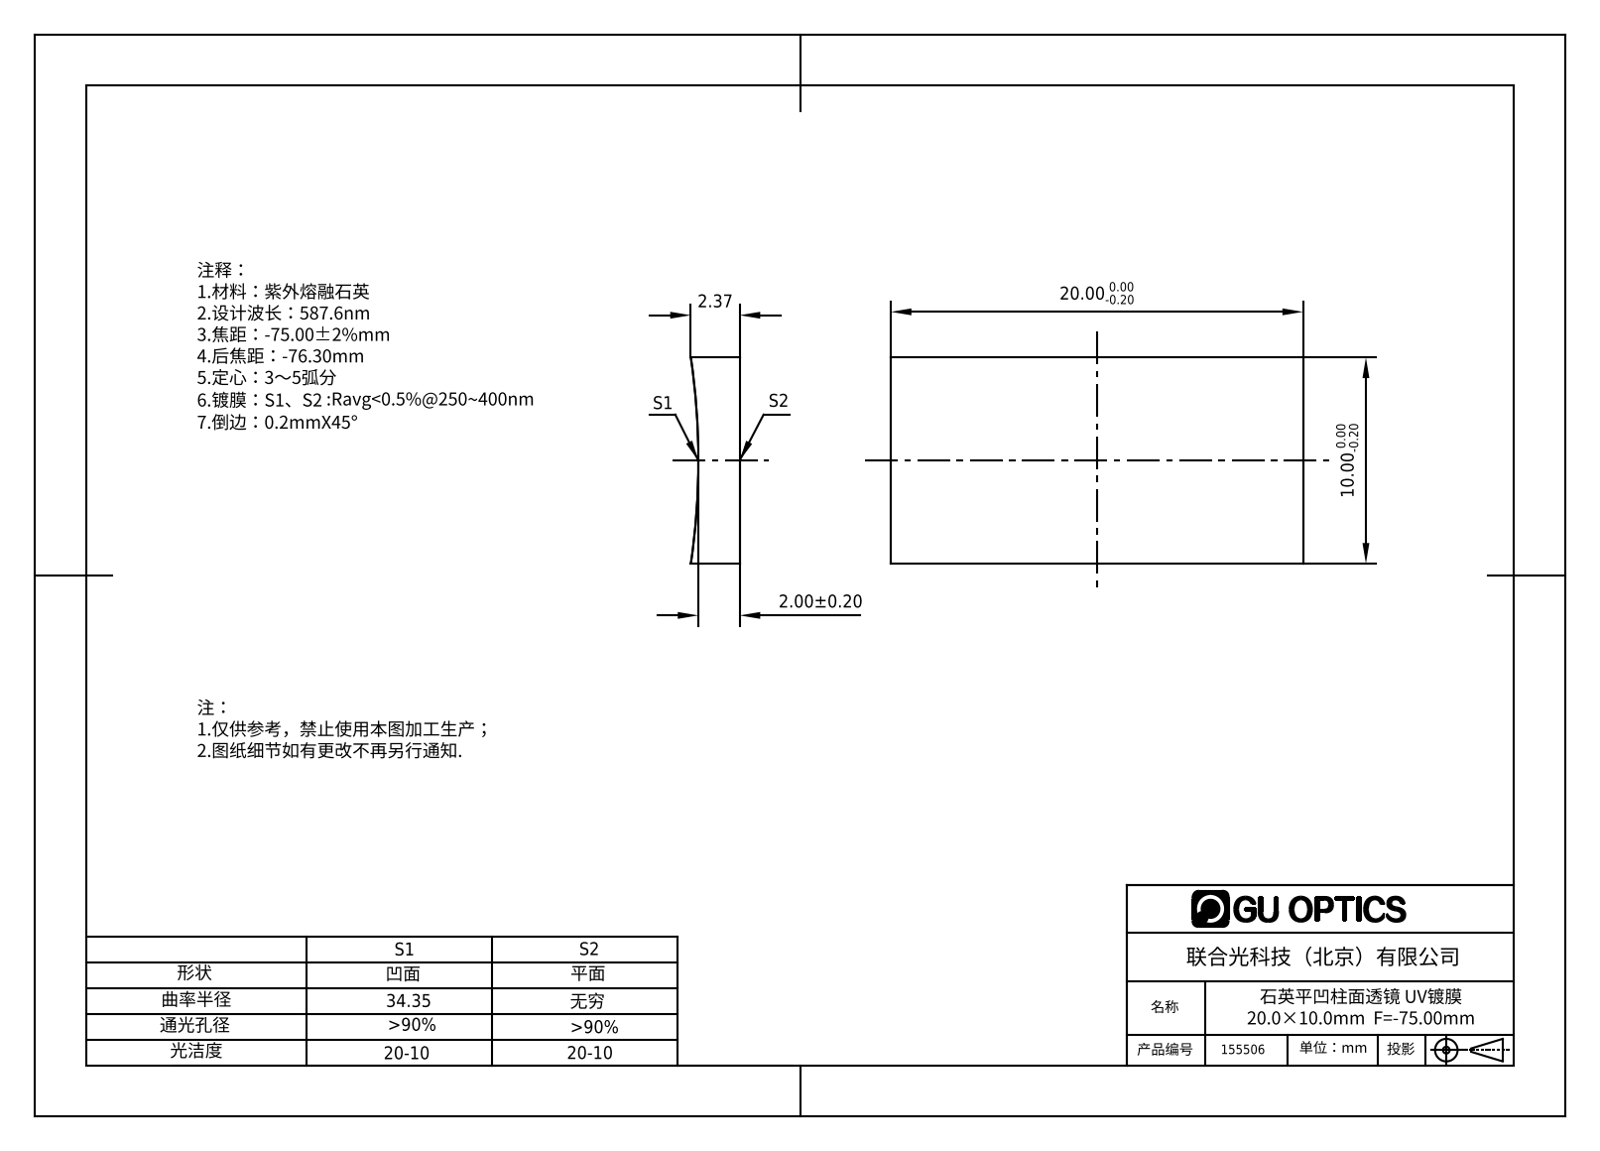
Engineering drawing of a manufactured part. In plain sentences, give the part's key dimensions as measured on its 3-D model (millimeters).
The part is named "155480". Its 3-D file was written by "SolidWorks 2016 (AUTOMOTIVE_DESIGN)". It is 1 solid with 6 faces: 5 planar, 1 cylindrical and 0 other. Overall it measures 20 by 10 by 2.37 millimeters. Its volume is 424 cubic millimeters and its surface area 538 square millimeters. Partial cylindrical surfaces (rounded edges, fillets, slot ends): 1 of radius 34.35. The main face-to-face distances are 10, 20.
